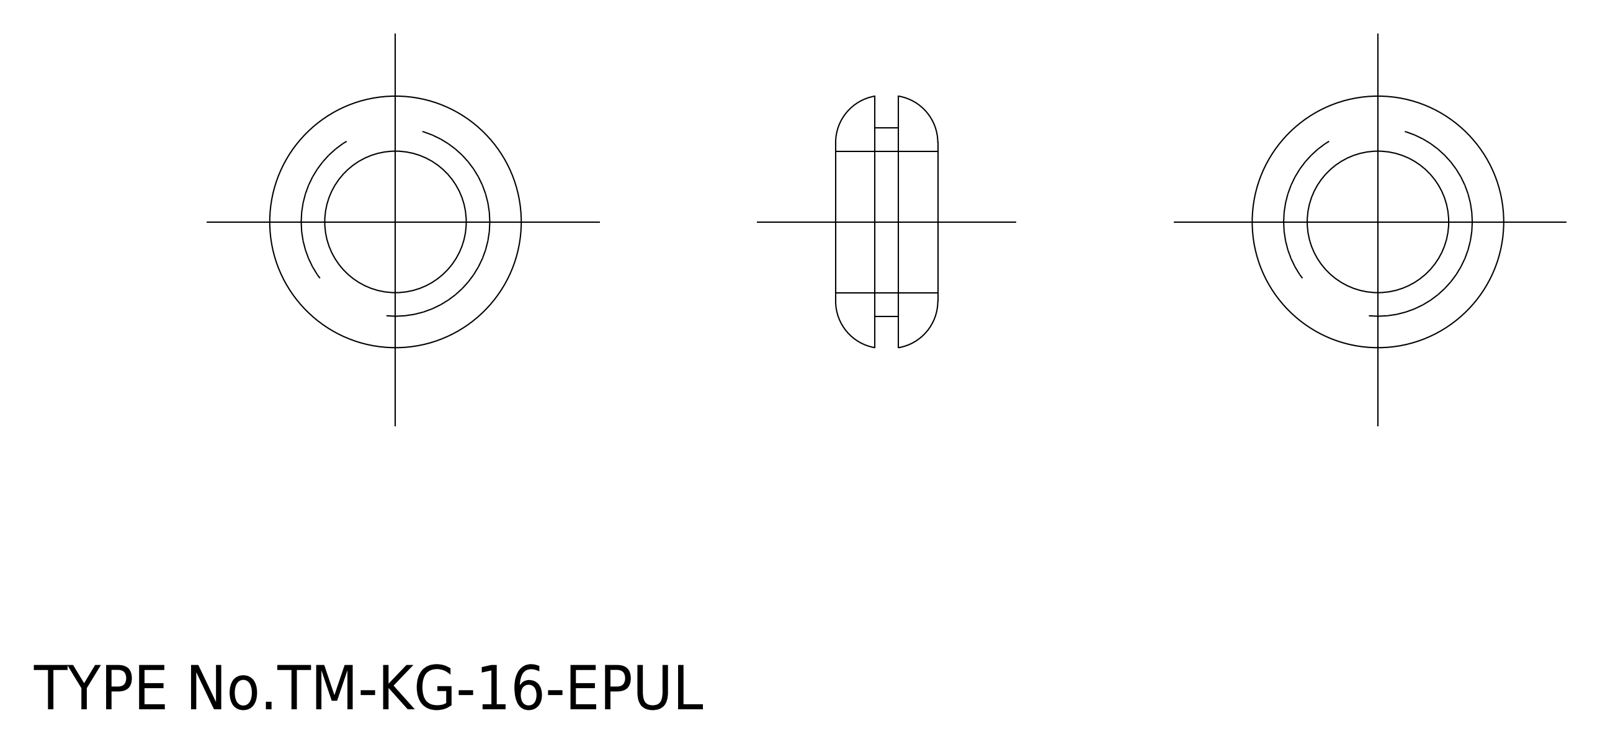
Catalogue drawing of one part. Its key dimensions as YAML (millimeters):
step_written_by: "spGate 15.6.1 (AUTOMOTIVE_DESIGN)"
units: millimeters
bodies: {solids: 1, faces: 12, planar: 4, cylindrical: 4, other: 4}
overall_size: [16, 16, 6.5]
volume: 594
surface_area: 810
round_holes:
  - {diameter: 9, count: 1}
round_bosses_or_shafts:
  - {diameter: 12, count: 1}
face_to_face_distances: [1.5, 2.5, 4, 6.5]
